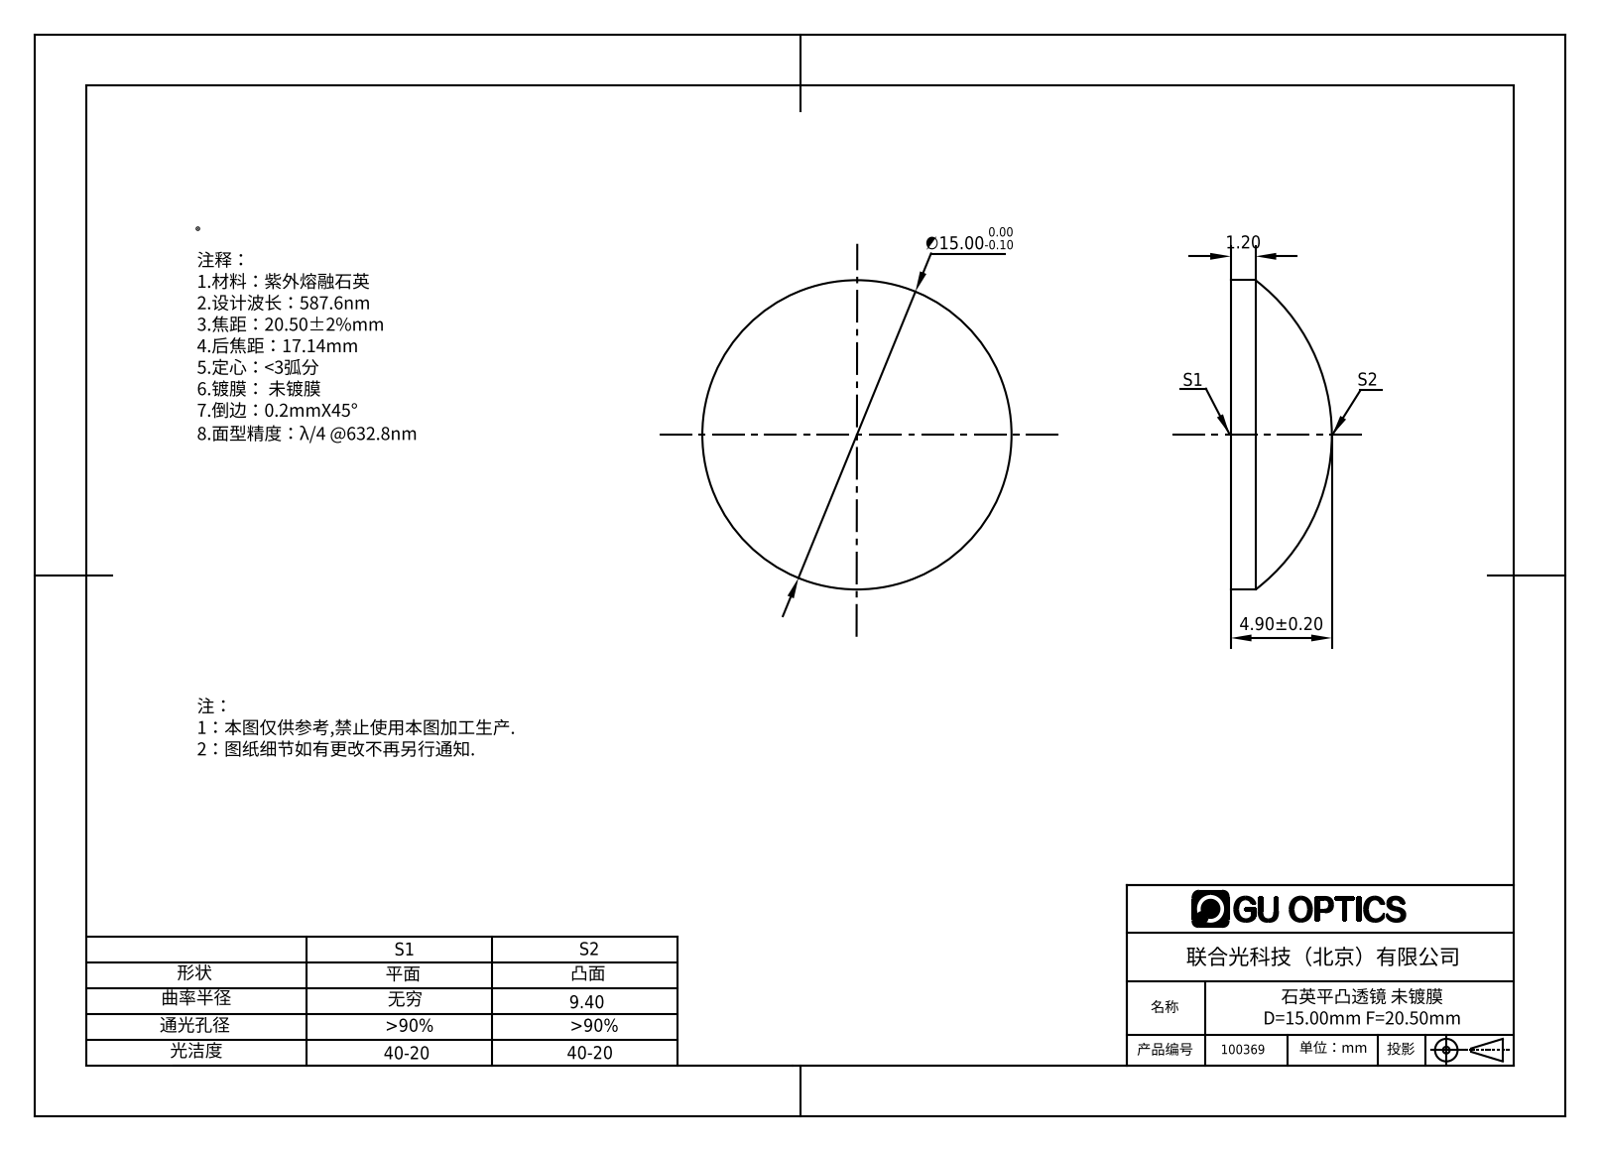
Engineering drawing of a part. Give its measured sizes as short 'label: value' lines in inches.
name: 100369
written by: SolidWorks 2016 (AUTOMOTIVE_DESIGN)
unit: in
bodies: 1 solid, 5 faces (1 planar, 2 cylindrical, 2 other)
size: 0.591 × 0.591 × 0.193
volume: 0.035 in³; area: 0.702 in²
bosses: 1× ⌀0.591
